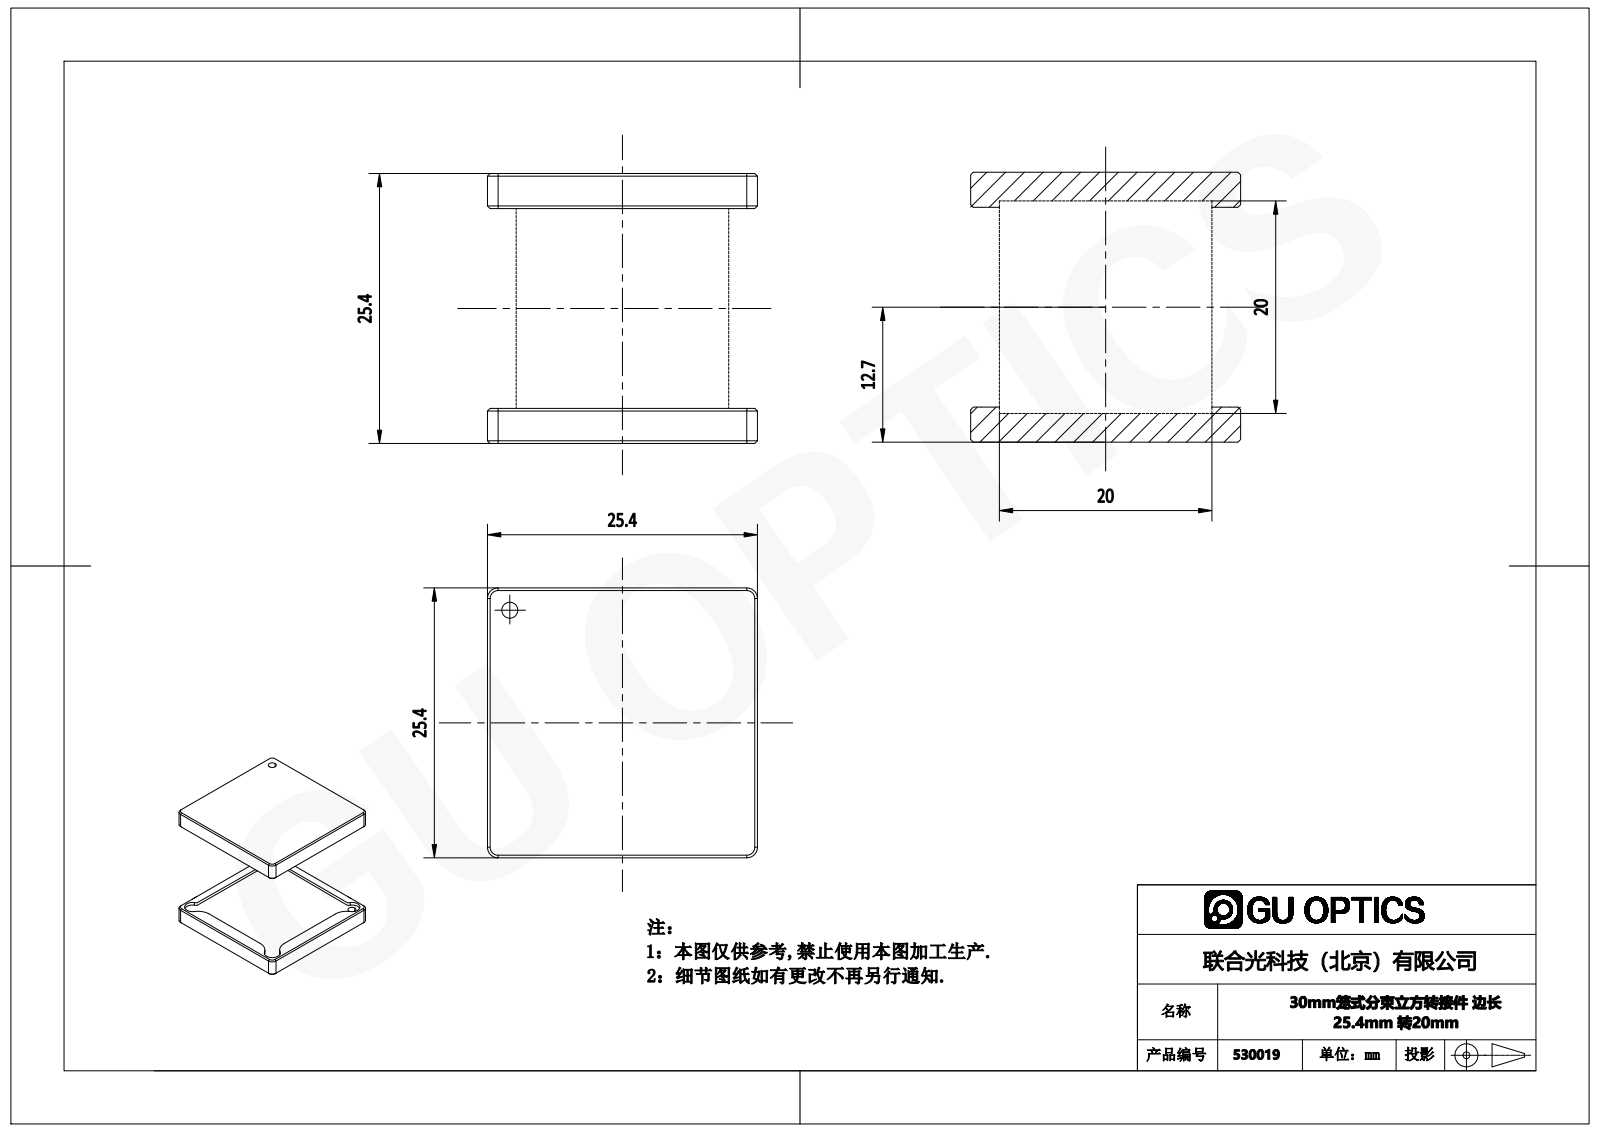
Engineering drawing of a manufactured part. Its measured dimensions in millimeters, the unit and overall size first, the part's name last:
Units: millimetres
Overall size (bounding box): 25.4 × 25.4 × 25.4
Round holes (diameter × count): ⌀1.5 ×2
Partial cylindrical surfaces — rounded edges, fillets, slot ends (radius × count): R3 ×8, R1 ×4, R1.5 ×4
Main face-to-face distances: 2.7, 22.7, 20, 25.4, 3.3, 22.1, 0.6, 19.4, 18.8, 4.31
Hole centre spacings: 21.2
Bodies: 0 solids, 90 faces (34 planar, 40 cylindrical, 16 other)
Part name (STEP PRODUCT): 1.6.4.51_ZSJ-1F20_分束镜安装座转接件，边长25.4mm(1.0英寸)转20mm
STEP written by: SolidWorks 2018 (AUTOMOTIVE_DESIGN)
